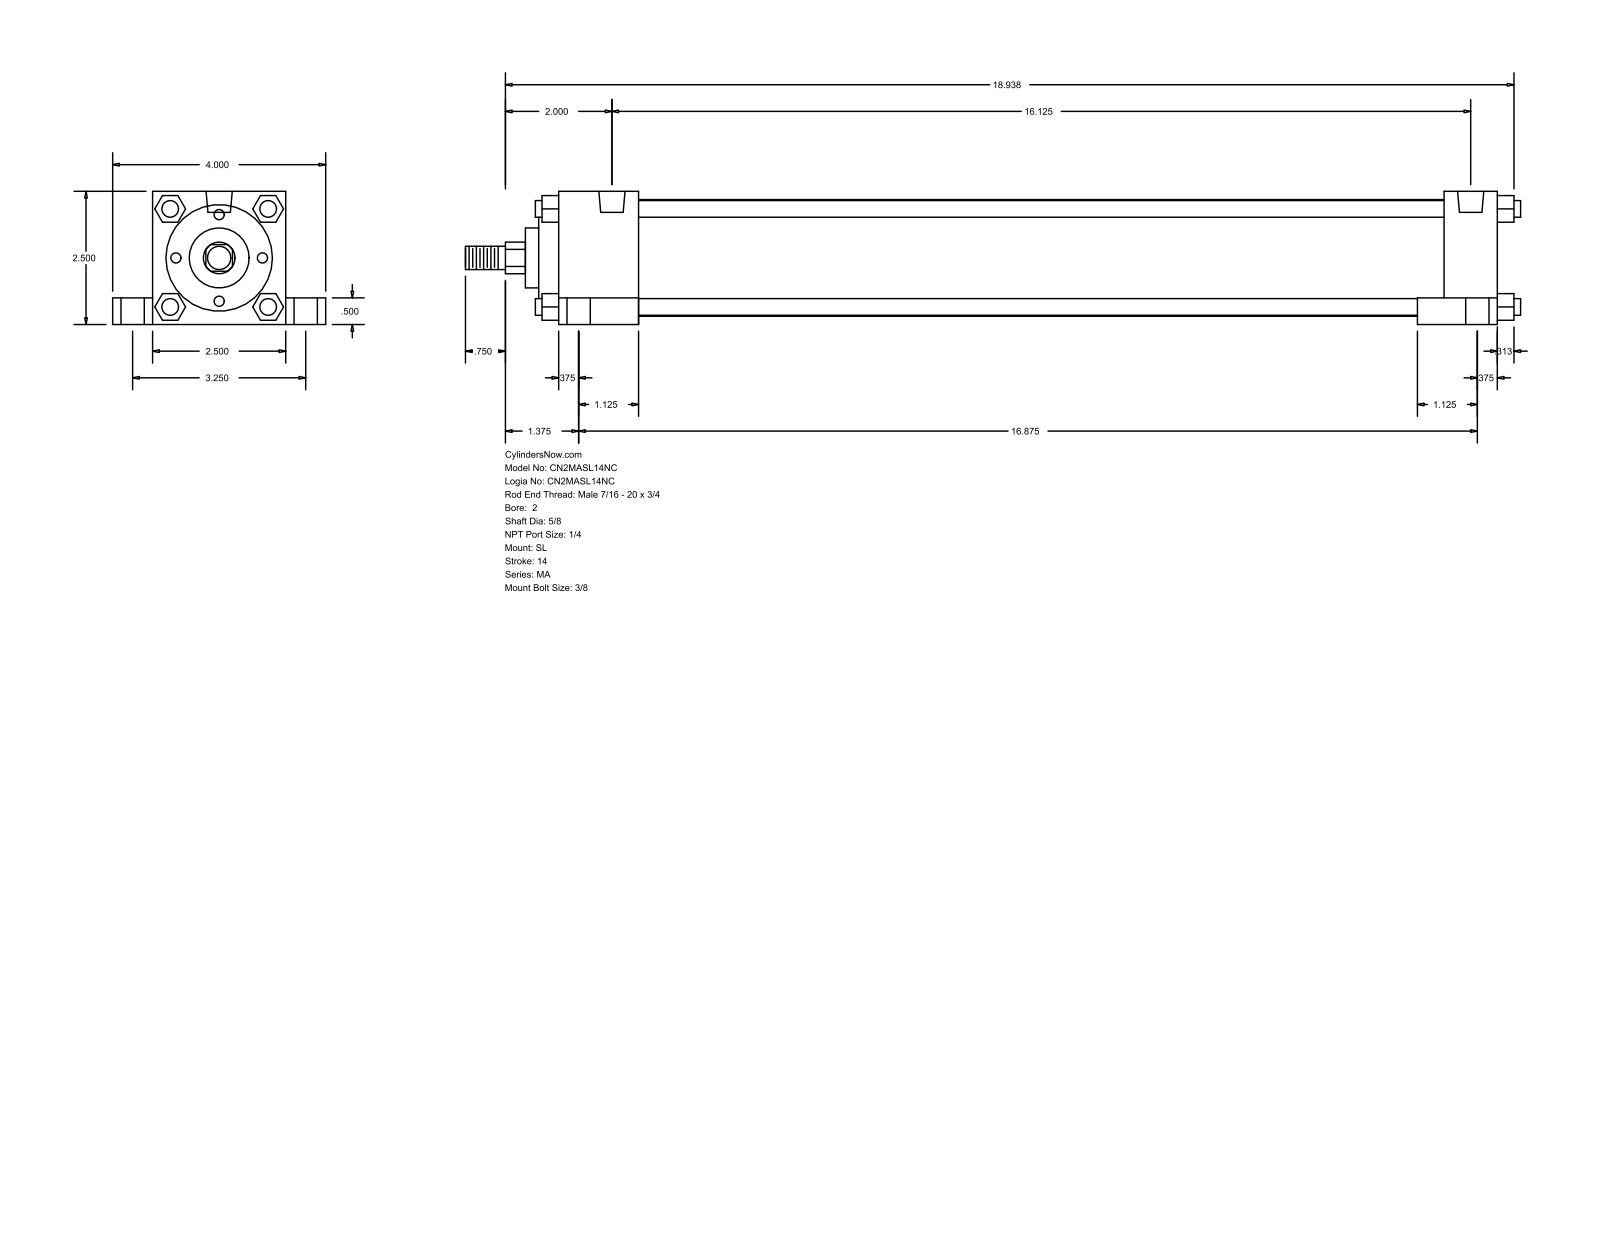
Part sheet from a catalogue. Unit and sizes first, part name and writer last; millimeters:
Units: millimetres
Overall size (bounding box): 503.24 × 101.6 × 63.5
Round holes (diameter × count): ⌀7.94 ×4, ⌀11.11 ×4, ⌀17.46 ×4, ⌀12.49 ×2
Round bosses / shafts (diameter × count): ⌀7.94 ×4, ⌀55.63 ×1, ⌀50.8 ×1, ⌀28.57 ×1, ⌀15.88 ×1, ⌀11.11 ×1
Partial cylindrical surfaces — rounded edges, fillets, slot ends (radius × count): R7.54 ×1
Main face-to-face distances: 63.5, 12.7, 9.52, 19.05, 82.55, 38.1, 50.8, 447.67, 409.57, 422.28
Hole centre spacings: 41.39, 44.22, 82.54, 409.58, 414.81, 427.46, 428.63, 436.5
Bodies: 0 solids, 150 faces (113 planar, 37 cylindrical, 0 other)
Part name (STEP PRODUCT): MA_SL__0200_0.625
STEP written by: GSSL Pune (CONFIG_CONTROL_DESIGN)
